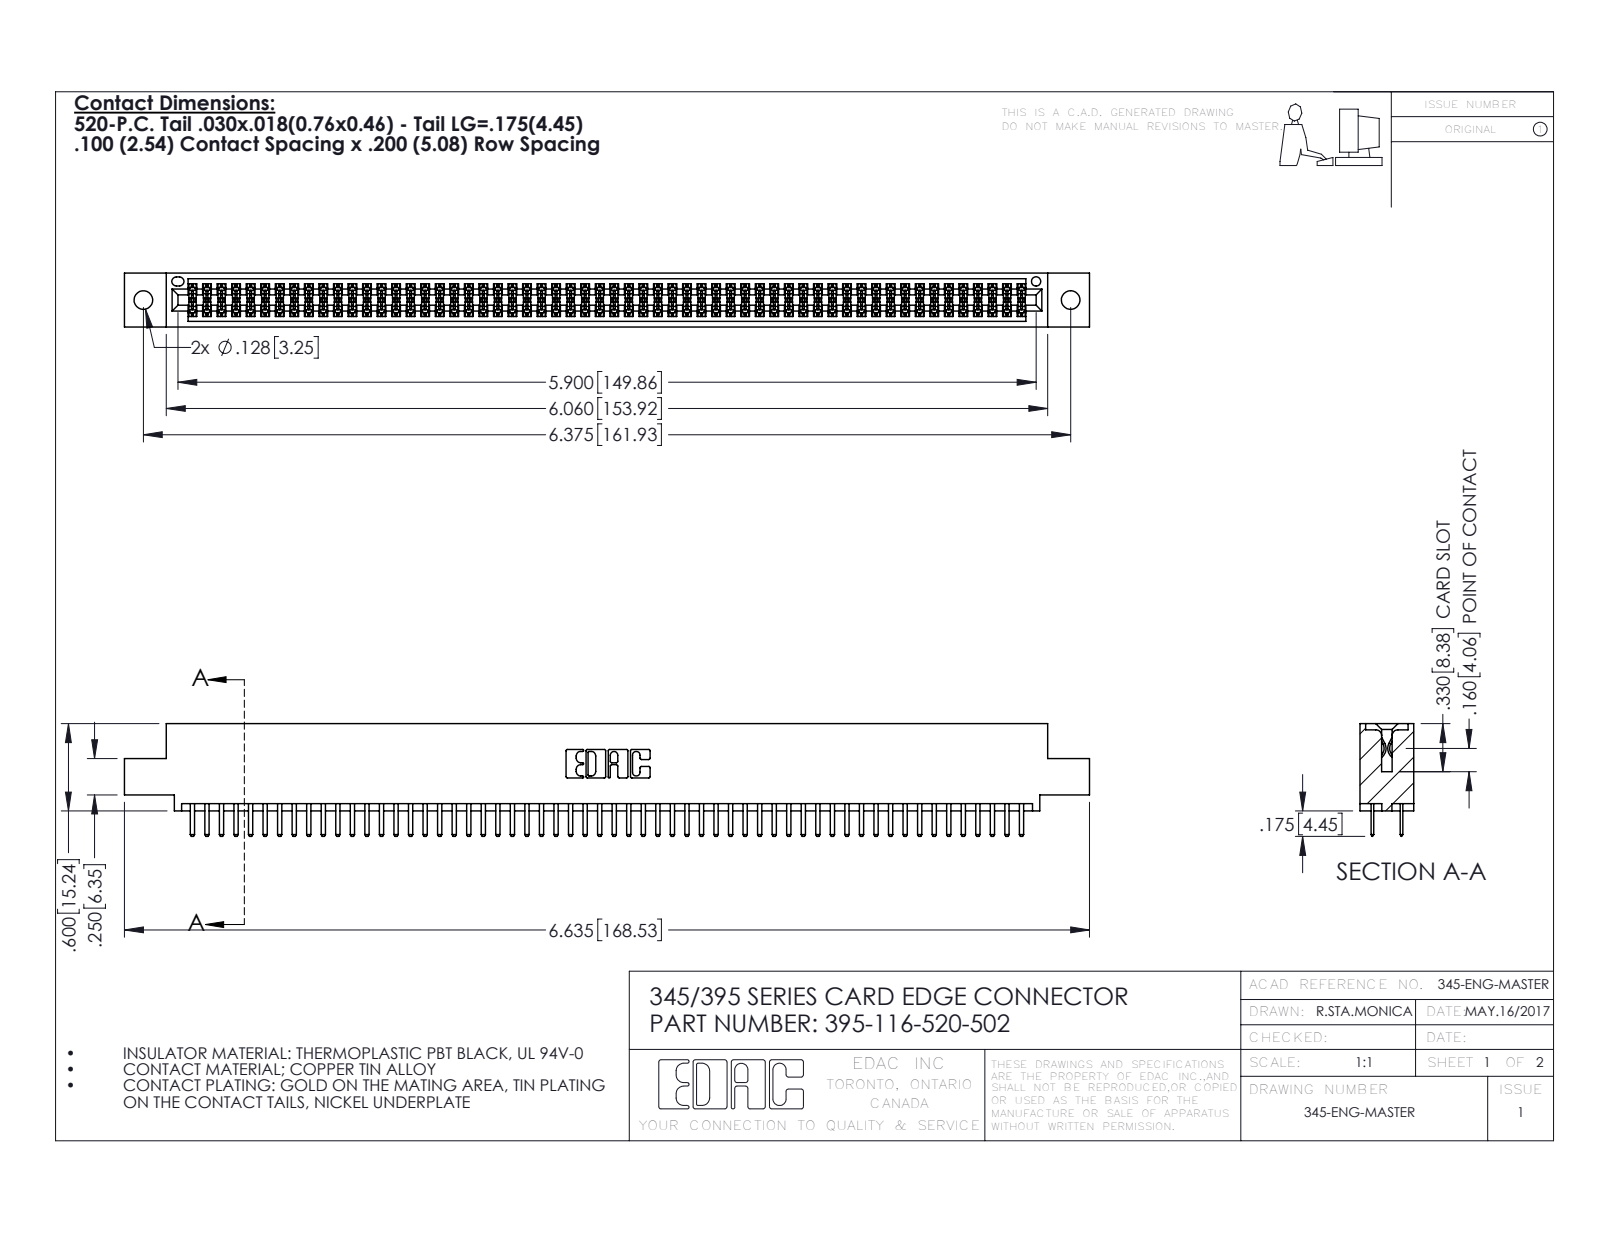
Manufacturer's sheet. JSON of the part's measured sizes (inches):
{"part_name": "345-292-001_345-293-120; 395-116-520-502; 345 Part_0.110 Offset - 0.128 Dia", "step_written_by": "SolidWorks 2016 (CONFIG_CONTROL_DESIGN)", "units": "inches", "bodies": {"solids": 117, "faces": 6394, "planar": 4144, "cylindrical": 2250, "other": 0}, "overall_size": [6.635, 0.775, 0.37], "volume_in3": 0.998, "surface_area_in2": 37.51, "round_holes": [[0.128, 2], [0.064, 1]], "partial_cylinders_radius": [[0.006, 174], [0.01, 120], [0.01, 22], [0.007, 6], [0.031, 6], [0.026, 3], [0.014, 2], [0.019, 2]], "face_to_face_distances": [0.298, 0.072, 0.2, 0.37, 0.098, 0.272, 0.025, 0.225, 0.022, 0.072], "hole_center_spacings": [0.27, 6.139, 6.375]}
